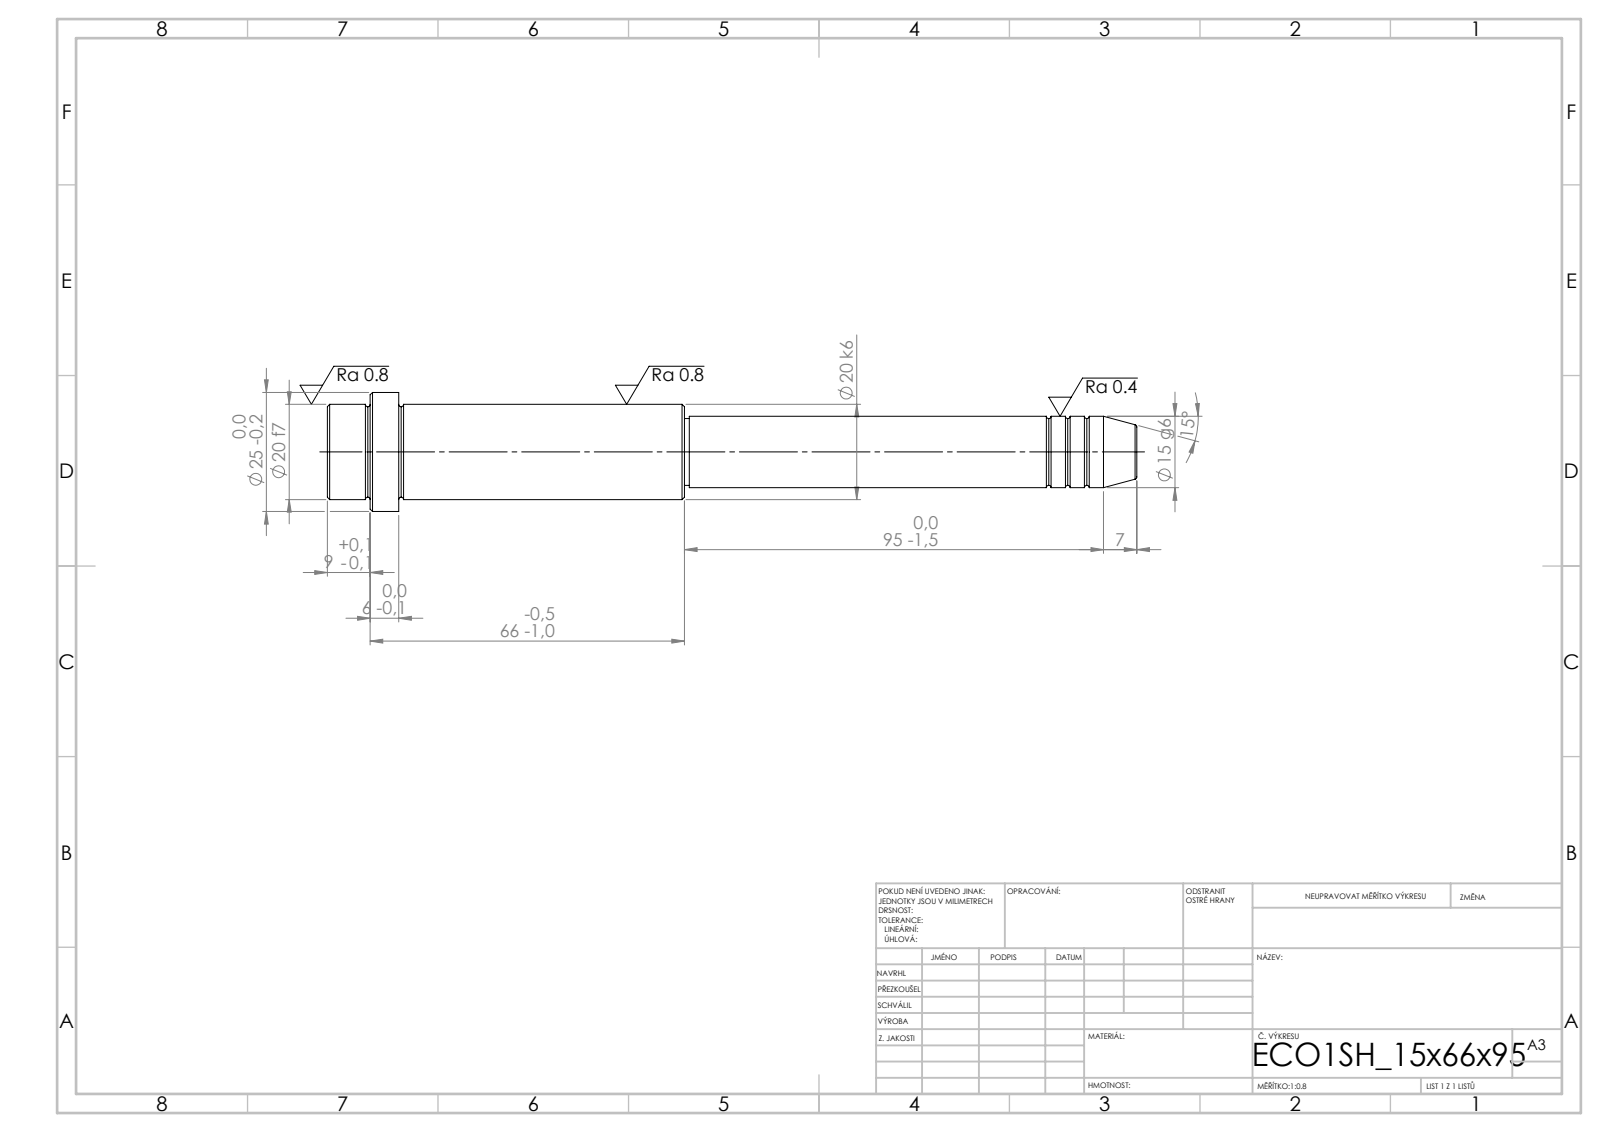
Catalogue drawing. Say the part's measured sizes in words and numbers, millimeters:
Its 3-D file was written by "SolidWorks 2019 (CONFIG_CONTROL_DESIGN)". It is 1 solid with 52 faces: 6 planar, 16 cylindrical and 30 other. Overall it measures 170 by 25 by 25 millimeters. Its volume is 40 975 cubic millimeters and its surface area 10 271 square millimeters. Round bosses or shafts: 1 of diameter 25, 1 of diameter 20, 1 of diameter 15, 1 of diameter 14. The main face-to-face distances are 15, 6, 9, 60, 66, 75, 95, 155, 161, 170.
